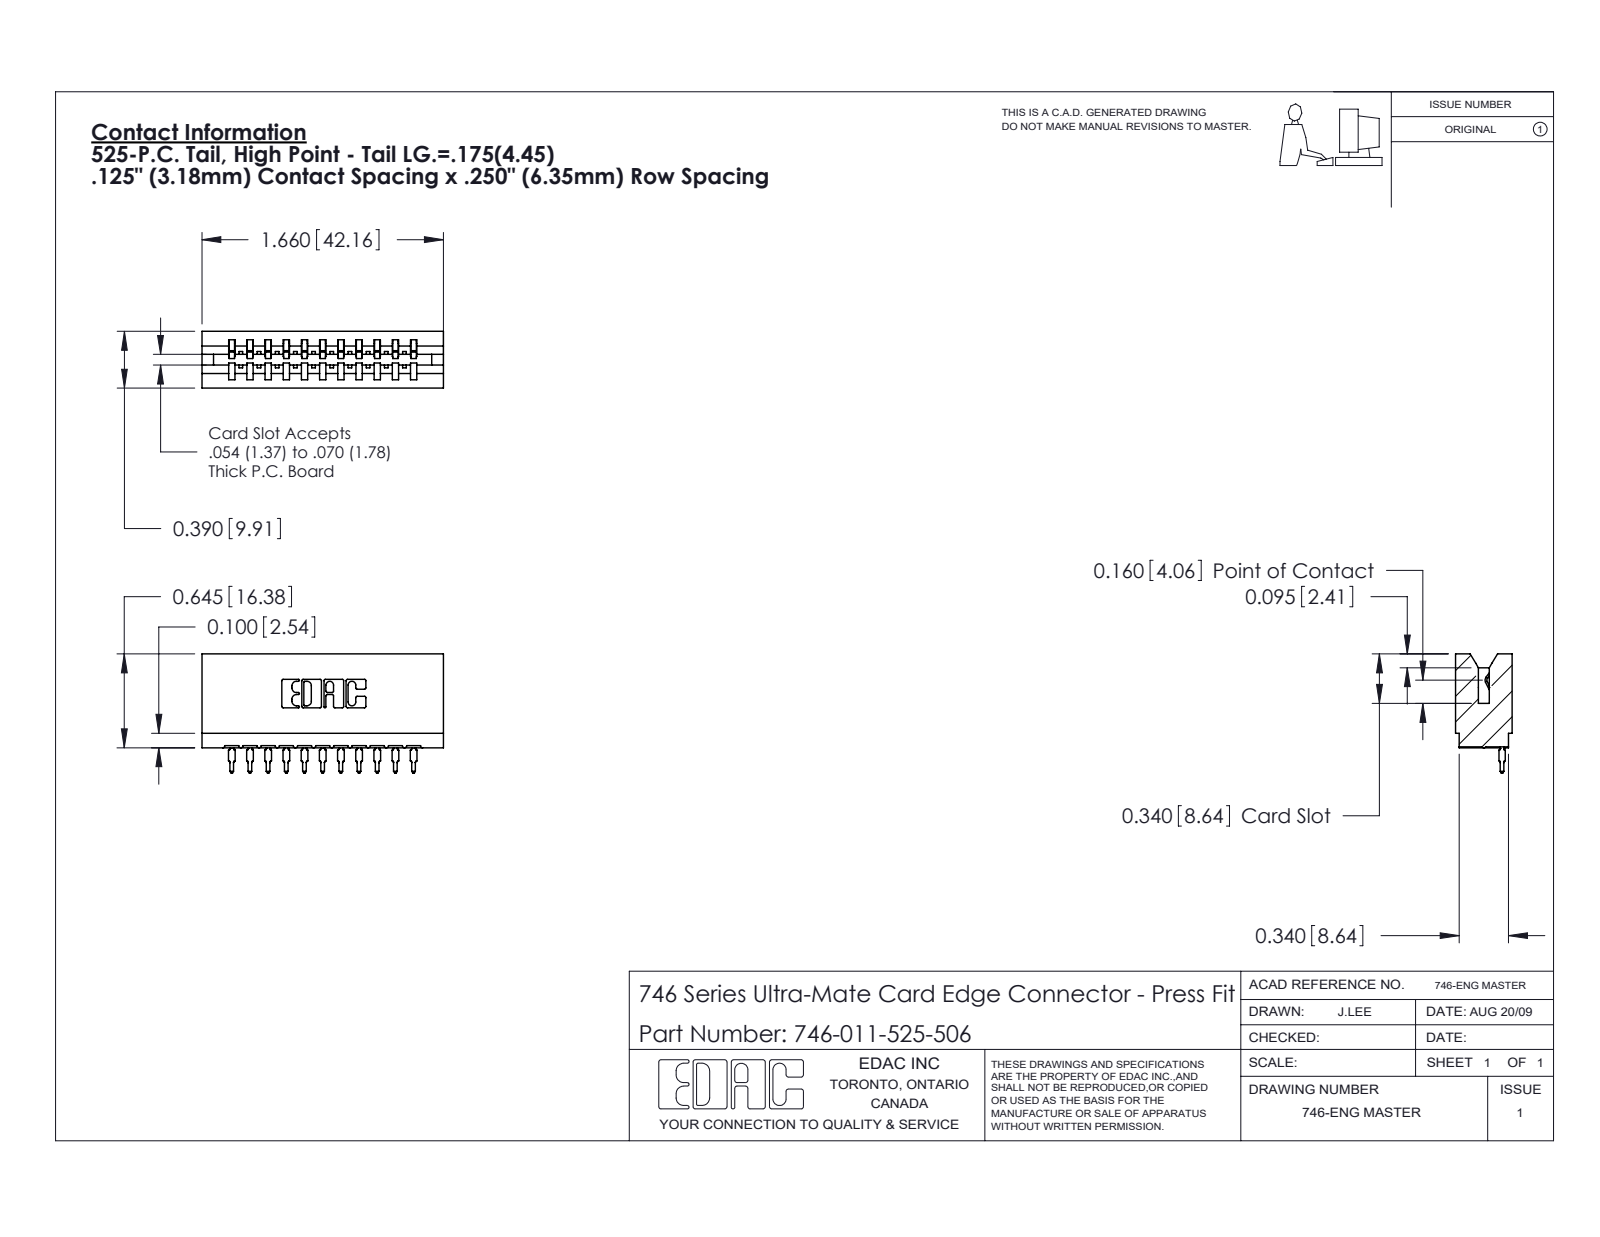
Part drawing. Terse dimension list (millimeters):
name: 746 Part_.340 Slot Depth - 06; 746-011-525-506; 746-292-001_525
written by: SolidWorks 2020 (CONFIG_CONTROL_DESIGN)
unit: mm
bodies: 12 solids, 1286 faces (749 planar, 251 cylindrical, 286 other)
size: 42.2 × 20.8 × 9.9
volume: 4 880 mm³; area: 6 072 mm²
rounds: 22× R0.3, 22× R0.5, 12× R0.4, 6× R0.2, 6× R0.8, 4× R0.1, 4× R0.3, 3× R0.7
face distances: 6.4, 12.7, 8.5, 3.2, 1.4, 1.1, 3.2, 7.4, 13.8, 9.9
